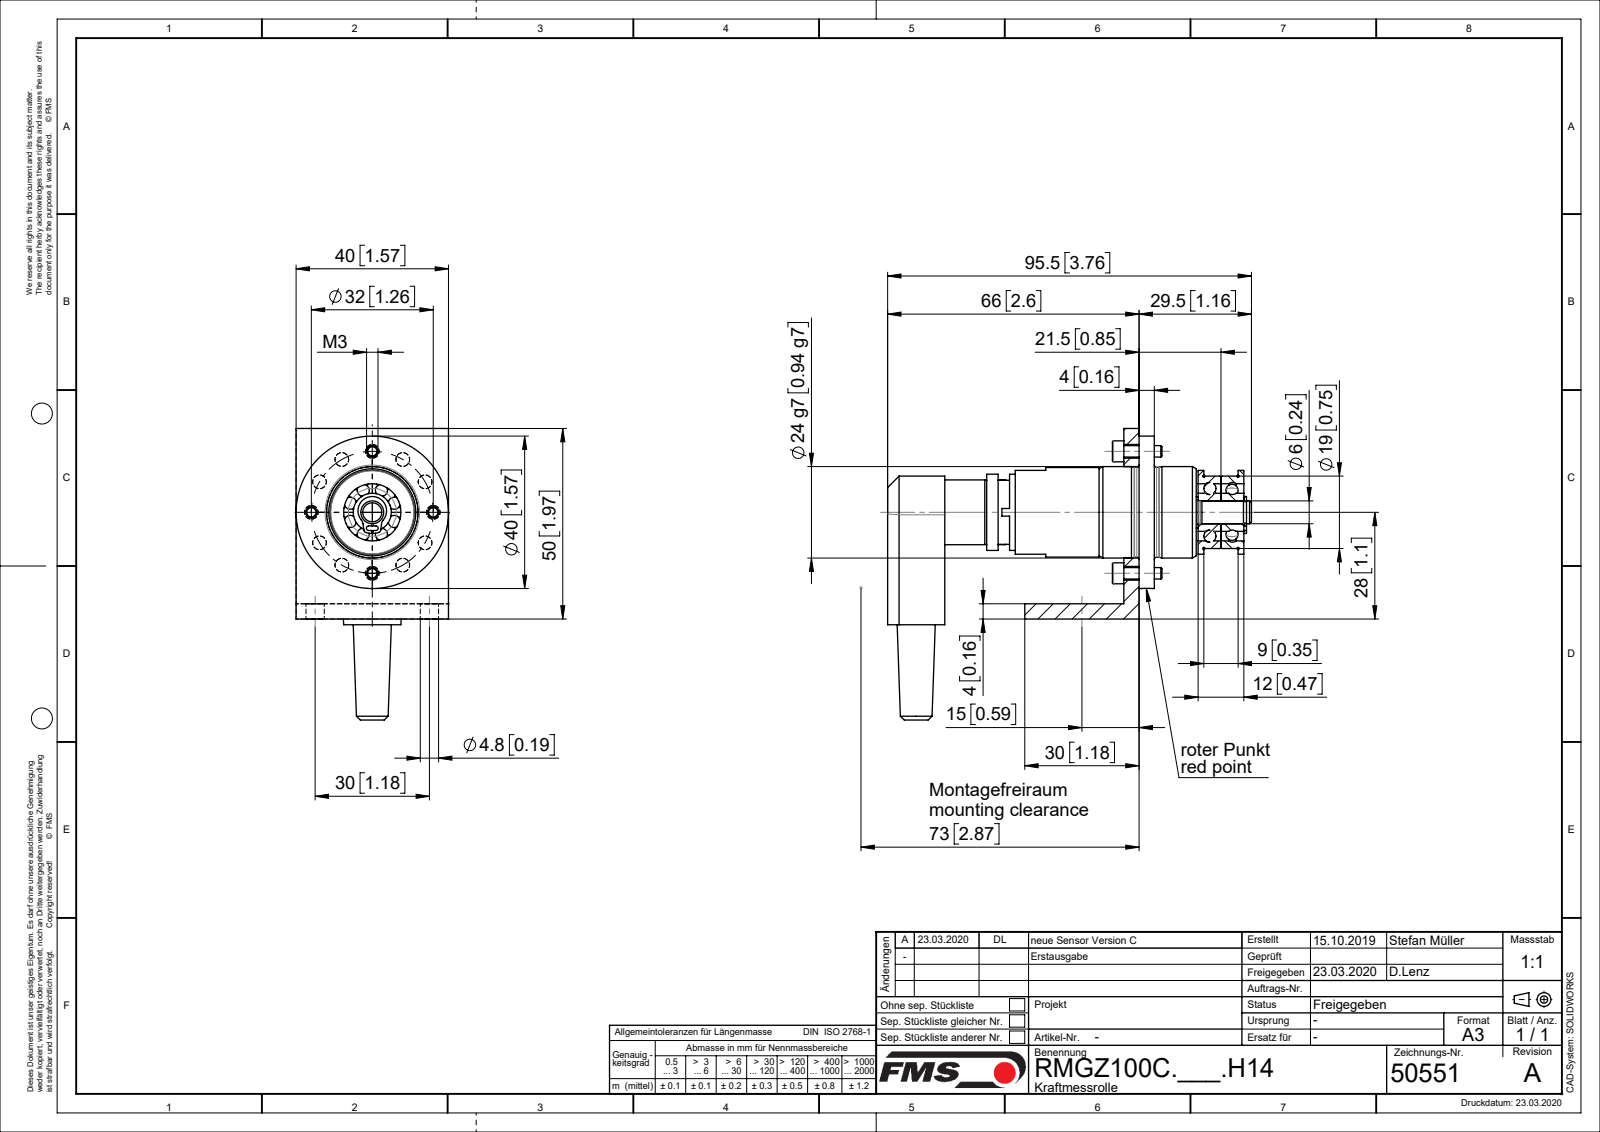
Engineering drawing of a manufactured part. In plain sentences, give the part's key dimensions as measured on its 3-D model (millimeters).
The part is named "R50551; R46750; TEIL1; R46749 (+8 more)". Its 3-D file was written by "Mechanical Desktop 2009 (CONFIG_CONTROL_DESIGN)". It is 13 solids with 389 faces: 107 planar, 170 cylindrical and 112 other. Overall it measures 95.5 by 76.5 by 40 millimeters. Its volume is 47 153 cubic millimeters and its surface area 31 033 square millimeters. Round holes: 12 of diameter 3.6, 5 of diameter 2, 4 of diameter 2.6, 2 of diameter 4.8, 1 of diameter 5.7, 1 of diameter 6, 1 of diameter 12, 1 of diameter 15, 1 of diameter 16, 1 of diameter 17, 1 of diameter 18.5. Round bosses or shafts: 5 of diameter 1.5, 4 of diameter 5.5, 4 of diameter 3, 1 of diameter 40, 1 of diameter 24, 1 of diameter 23.5, 1 of diameter 22, 1 of diameter 20. Partial cylindrical surfaces (rounded edges, fillets, slot ends): 1 of radius 1.5, 1 of radius 9. The main face-to-face distances are 4, 15, 6, 8, 66, 12.5, 10, 25.5, 19, 23.5. The hole center spacings are 16, 8.28, 22.63, 27.71, 30.91, 15.99, 19.11, 32.
